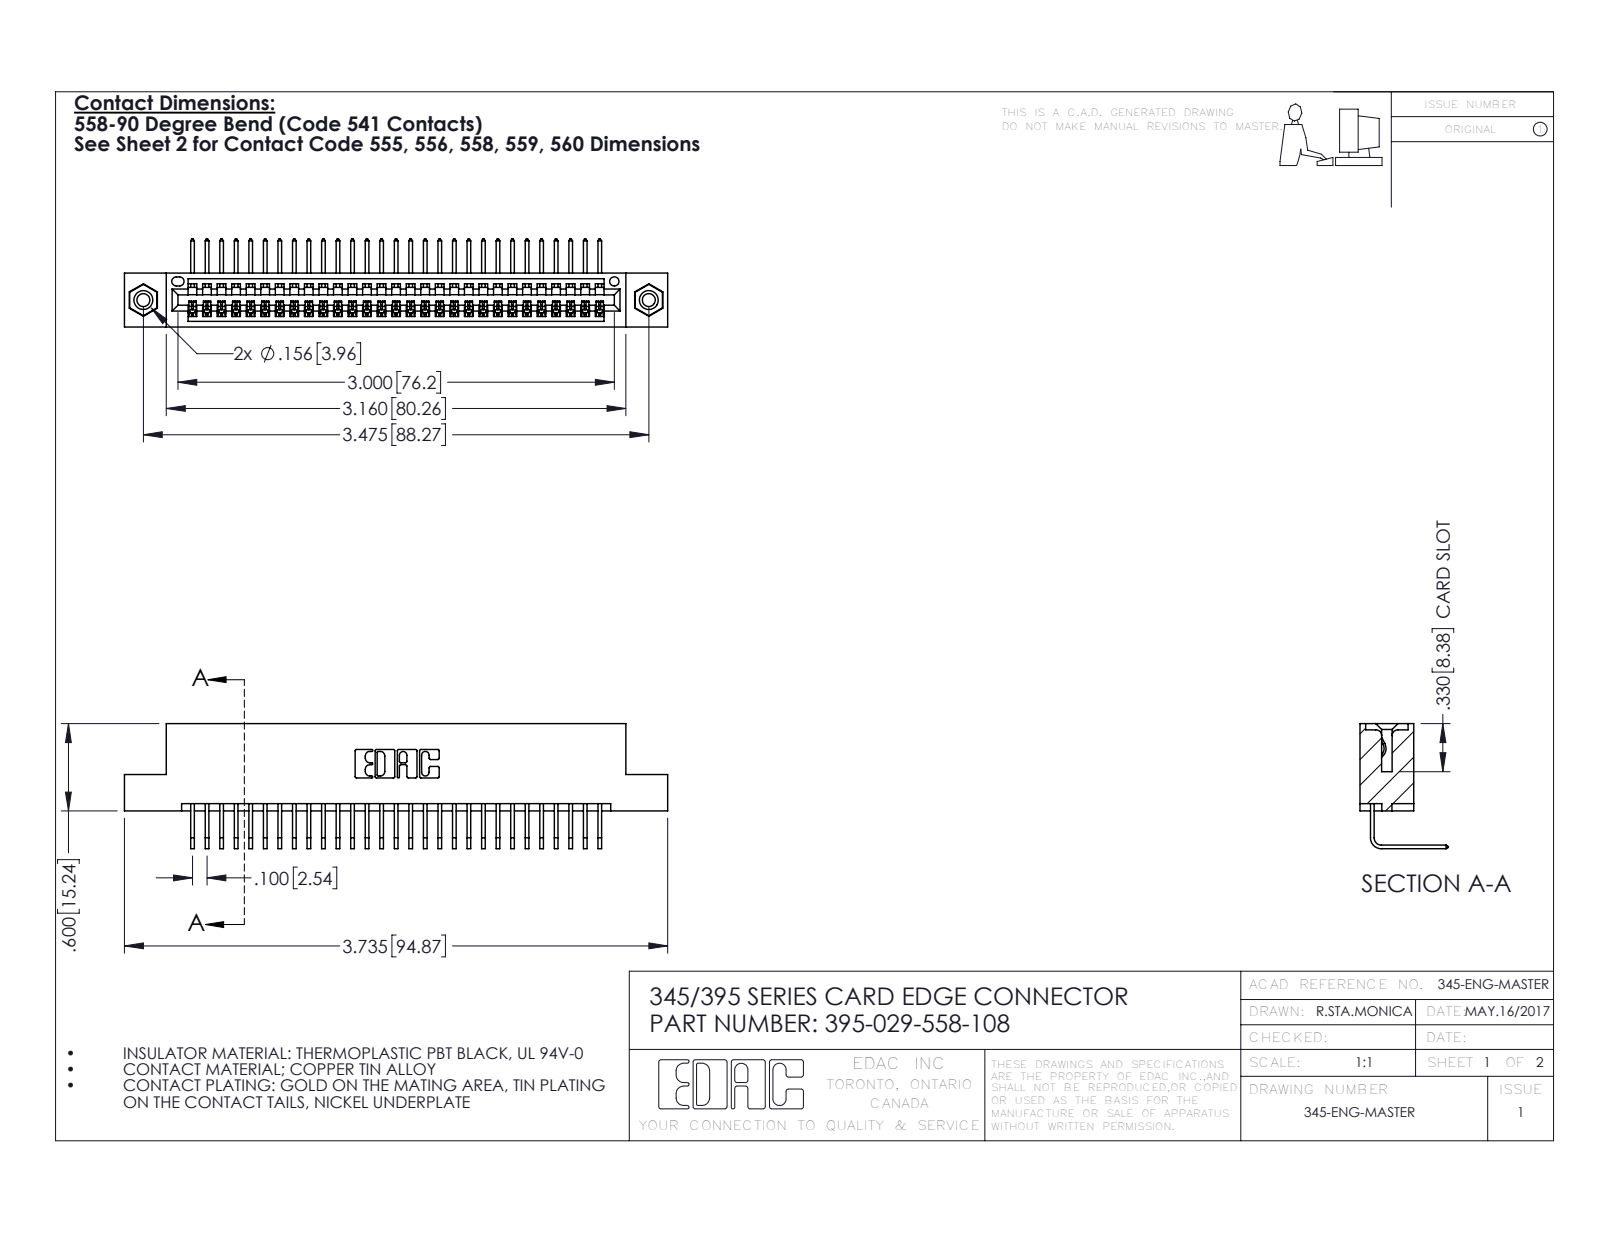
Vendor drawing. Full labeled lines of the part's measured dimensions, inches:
Part name (STEP PRODUCT): 395-029-558-108; 345-250-001_345-250-003-102; 345 Part_Flush Mounting Lugs - 0.156 Dia-TI; 345-292-001_558 Tail - 2
STEP written by: SolidWorks 2016 (CONFIG_CONTROL_DESIGN)
Units: inches
Bodies: 32 solids, 1926 faces (1330 planar, 580 cylindrical, 16 other)
Overall size (bounding box): 3.735 × 0.859 × 0.605
Volume: 0.549 in³ · Surface area: 19.16 in²
Round holes (diameter × count): ⌀0.089 ×2, ⌀0.125 ×2, ⌀0.156 ×2, ⌀0.064 ×1
Round bosses / shafts (diameter × count): ⌀0.155 ×2
Partial cylindrical surfaces — rounded edges, fillets, slot ends (radius × count): R0.006 ×58, R0.01 ×22, R0.007 ×6, R0.031 ×6, R0.026 ×3, R0.031 ×2, R0.04 ×2, R0.014 ×1
Main face-to-face distances: 0.072, 0.298, 0.2, 0.37, 0.098, 0.272, 0.025, 0.225, 0.149, 0.072
Hole centre spacings: 0.27, 3.24, 3.475
